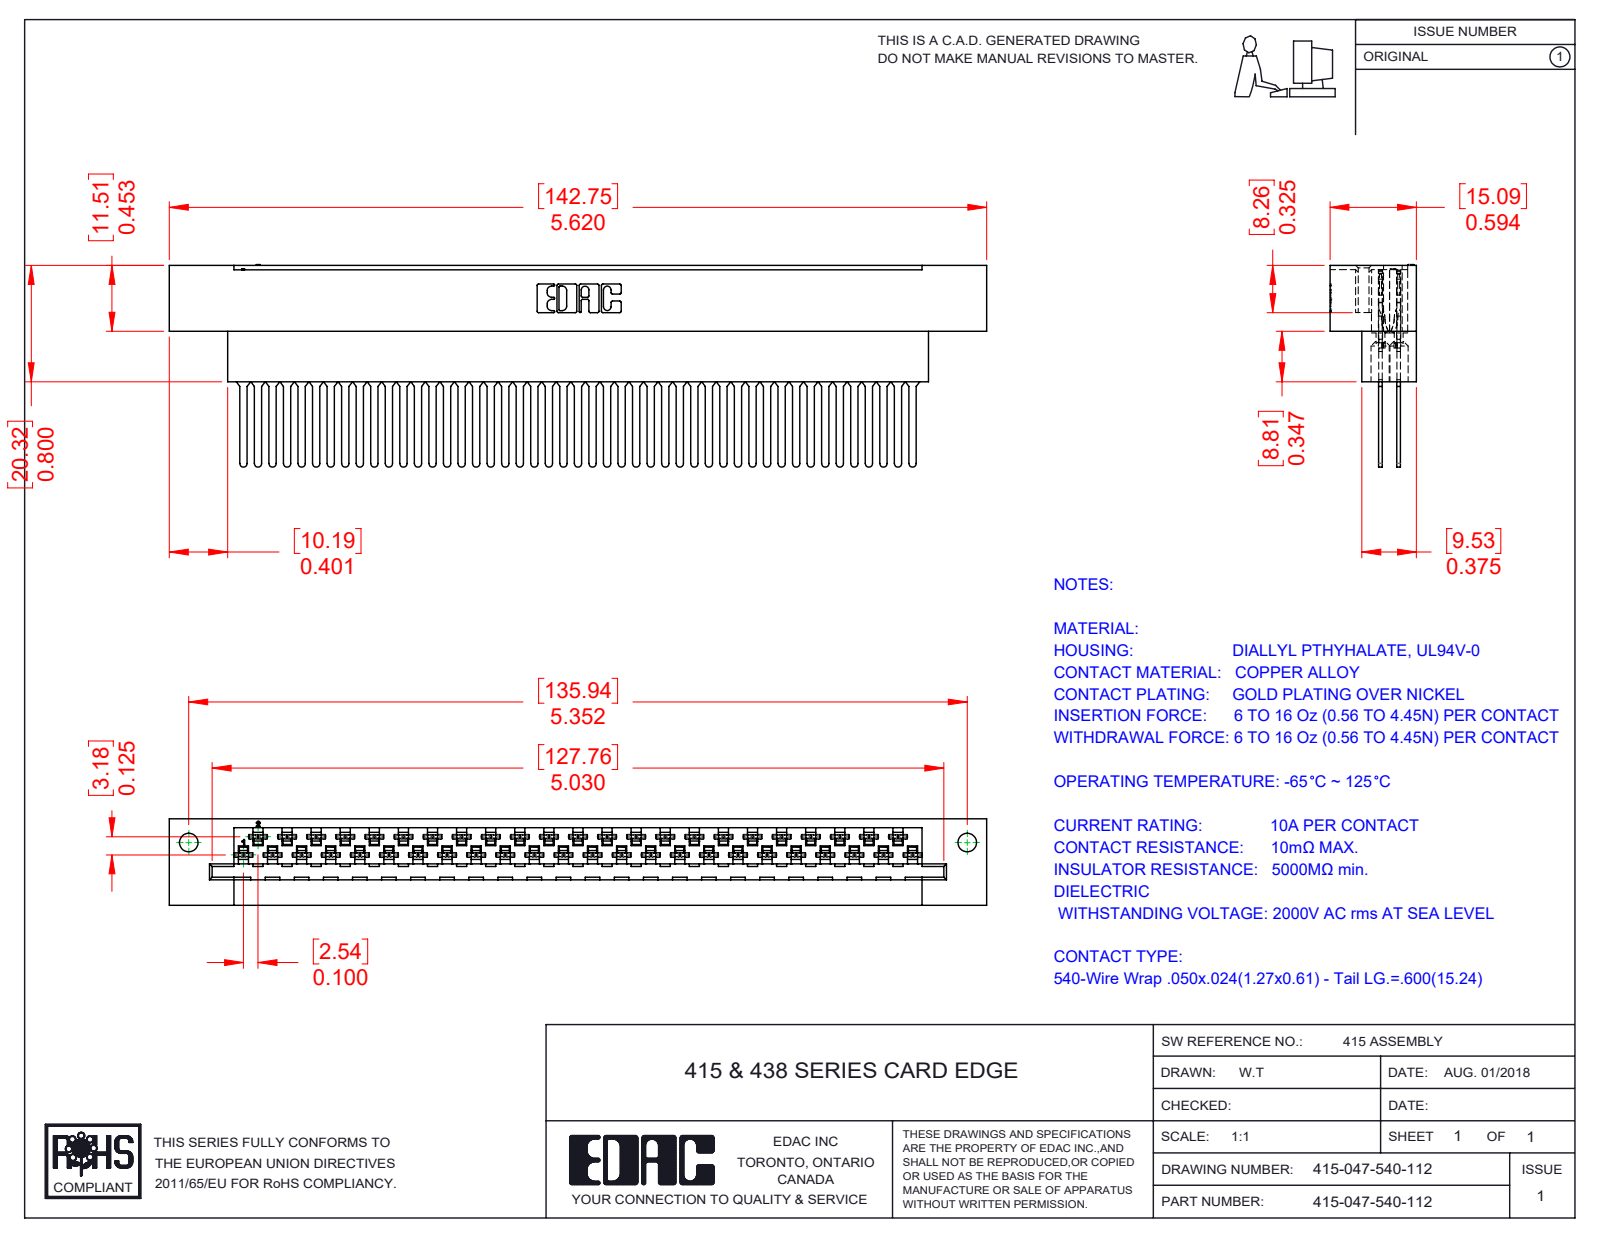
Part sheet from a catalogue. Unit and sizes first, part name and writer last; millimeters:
Units: millimetres
Overall size (bounding box): 142.75 × 35.34 × 15.09
Round holes (diameter × count): ⌀1.27 ×47, ⌀3.3 ×47, ⌀3.25 ×2
Partial cylindrical surfaces — rounded edges, fillets, slot ends (radius × count): R0.3 ×188, R0.56 ×188, R0.18 ×94, R0.2 ×94, R0.41 ×94, R2.03 ×94, R0.64 ×47, R0.25 ×22
Main face-to-face distances: 3.18, 0.61, 1.88, 1.27, 15.09, 6.61, 8.48, 6, 9.09, 2.82
Hole centre spacings: 5.08, 10.16, 15.24, 20.32, 25.4, 30.48, 35.56, 2.54
Volume: 26 936 mm³ · Surface area: 31 975 mm²
Bodies: 48 solids, 4750 faces (3039 planar, 1266 cylindrical, 445 other)
Part name (STEP PRODUCT): 516-290-001_540; 415-210-001_415-210-047-112; 415-047-540-112
STEP written by: SolidWorks 2016 (CONFIG_CONTROL_DESIGN)
